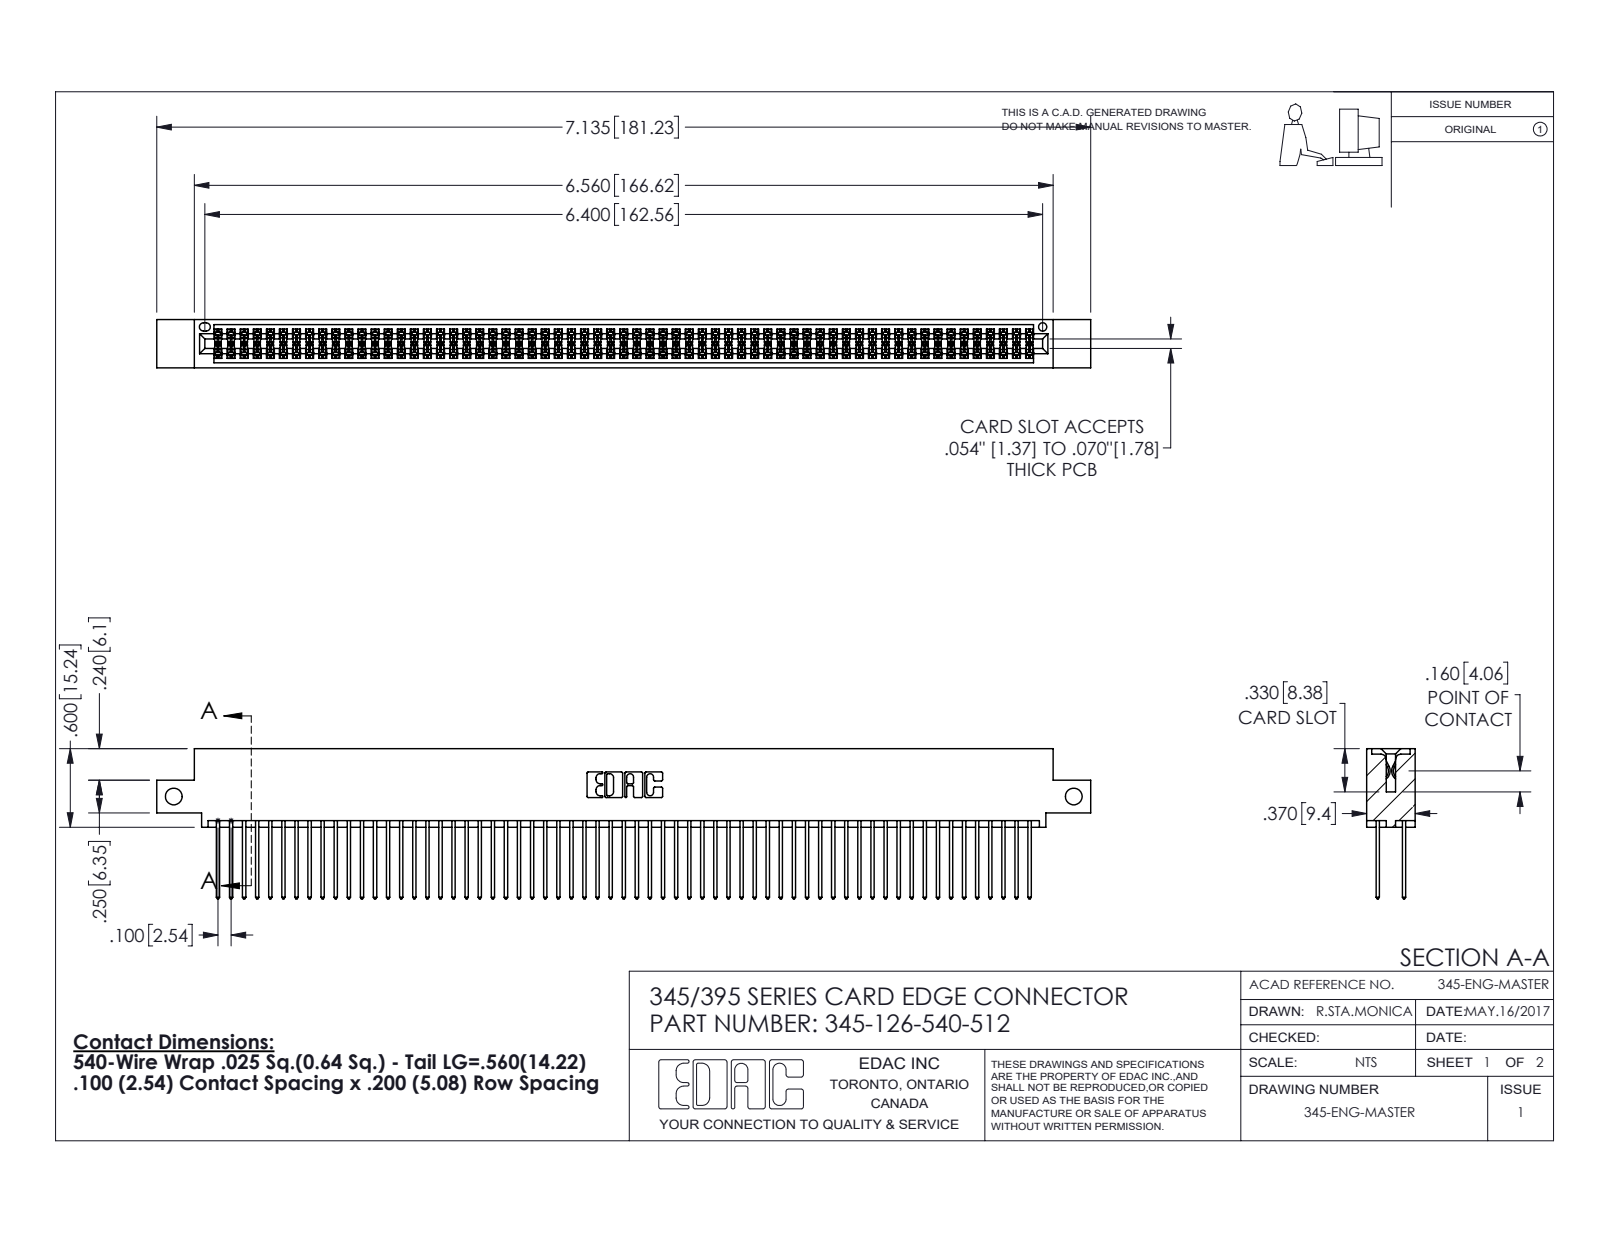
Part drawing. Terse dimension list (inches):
name: 345 Part_0.110 Offset - Side Mount; 345-292-001_345-293-140; 345-126-540-512
written by: SolidWorks 2016 (CONFIG_CONTROL_DESIGN)
unit: in
bodies: 127 solids, 6430 faces (4242 planar, 2188 cylindrical, 0 other)
size: 7.135 × 1.147 × 0.37
volume: 1.106 in³; area: 45.51 in²
holes: 2× ⌀0.128, 1× ⌀0.064
rounds: 189× R0.006, 126× R0.01, 22× R0.01, 6× R0.007, 6× R0.031, 3× R0.026, 2× R0.014, 2× R0.019
face distances: 0.298, 0.072, 0.2, 0.098, 0.272, 0.025, 0.225, 0.37, 0.175, 0.149
hole spacings: 6.875
